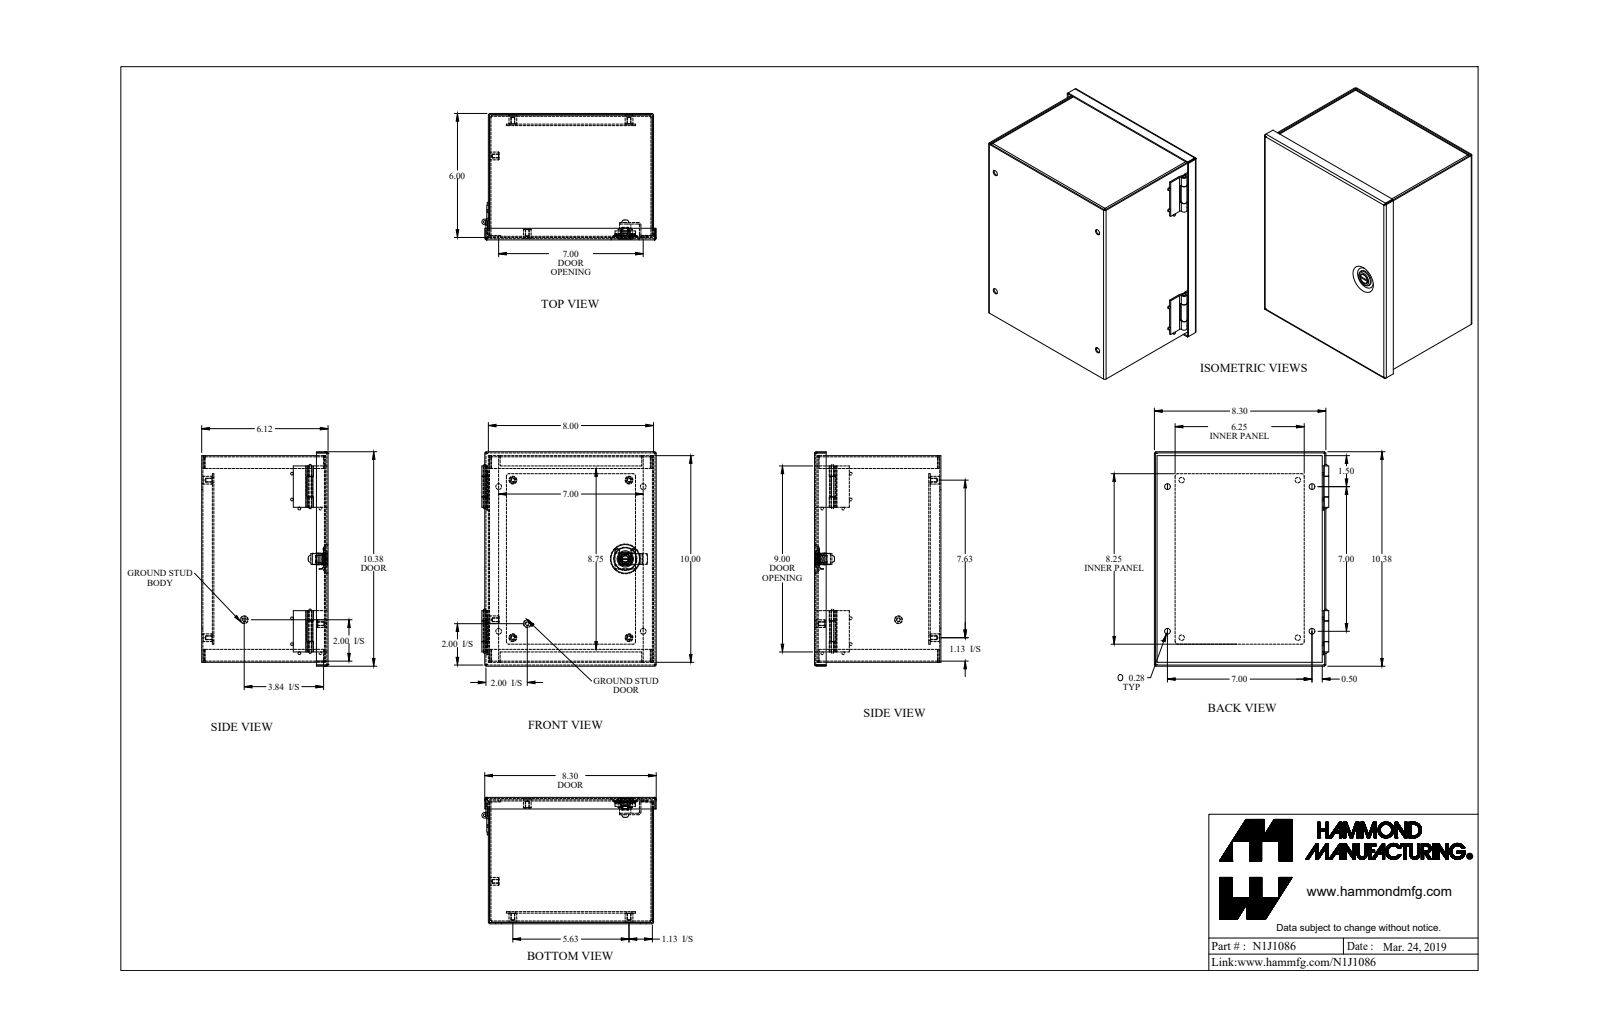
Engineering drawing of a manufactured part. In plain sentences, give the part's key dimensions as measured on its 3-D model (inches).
The part is named "N1J1086". Its 3-D file was written by "SolidWorks 2018 (AUTOMOTIVE_DESIGN)". It is 18 solids with 477 faces: 224 planar, 188 cylindrical and 65 other. Overall it measures 10.38 by 8.443 by 6.118 inches. Its volume is 29.4 cubic inches and its surface area 1 007 square inches. Round holes: 6 of diameter 0.156, 4 of diameter 0.265, 4 of diameter 0.28, 1 of diameter 0.125, 1 of diameter 0.319, 1 of diameter 0.476. Round bosses or shafts: 8 of diameter 0.131, 6 of diameter 0.375, 1 of diameter 0.787, 1 of diameter 0.547, 1 of diameter 0.472, 1 of diameter 0.469, 1 of diameter 0.366, 1 of diameter 0.32. Partial cylindrical surfaces (rounded edges, fillets, slot ends): 16 of radius 0.029, 16 of radius 0.086, 4 of radius 0.012, 4 of radius 0.1, 4 of radius 0.125, 2 of radius 0.036, 2 of radius 0.079, 2 of radius 0.25. The main face-to-face distances are 0.057, 6.061, 7.943, 9.943, 6.004, 6.118, 8, 7.886, 0.072, 0.517. The hole center spacings are 0.755, 6.32, 7, 7.345, 9.66, 3.607, 3.817, 5.625.
